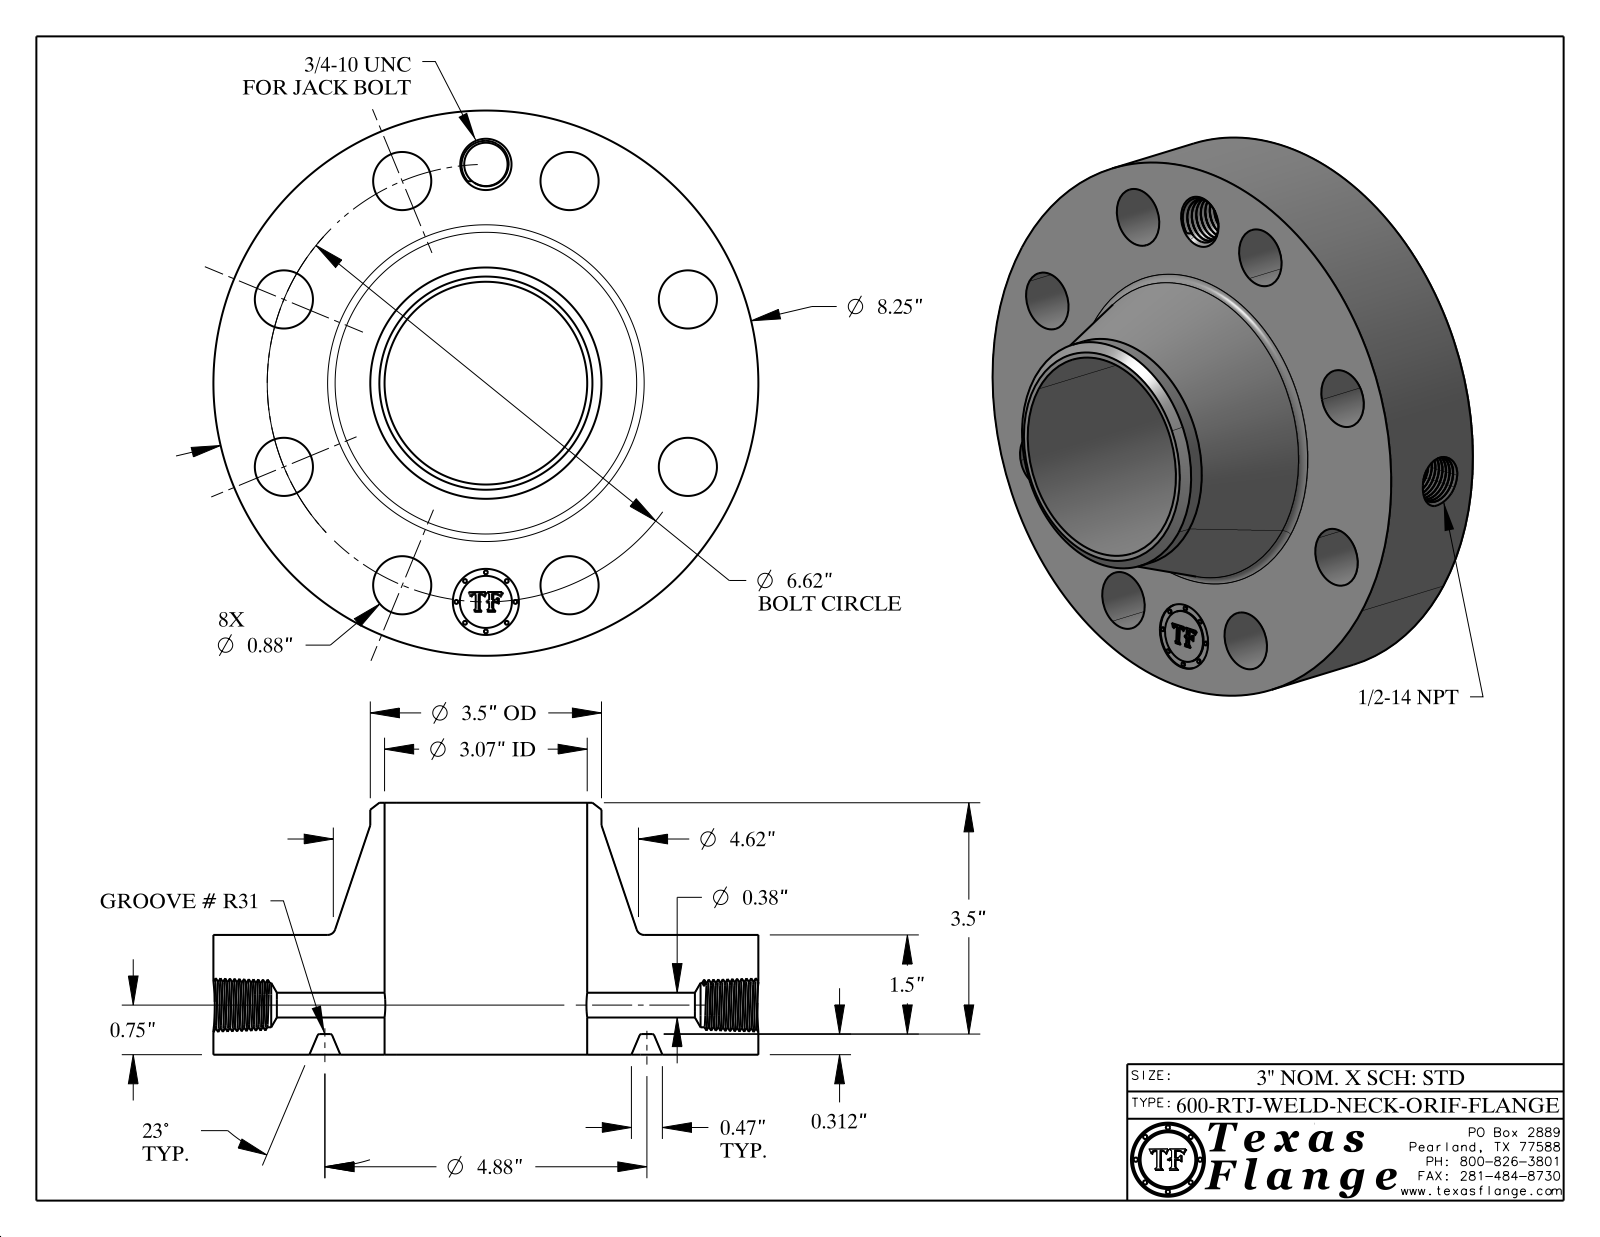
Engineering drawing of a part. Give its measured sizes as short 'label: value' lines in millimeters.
name: 600-RTJ-WELD-NECK
written by: CATIA V5 STEP AP214 (AUTOMOTIVE_DESIGN)
unit: mm
bodies: 1 solid, 795 faces (370 planar, 96 cylindrical, 329 other)
size: 209.6 × 209.6 × 96.8
volume: 1 331 000 mm³; area: 158 400 mm²
holes: 8× ⌀22.4, 1× ⌀9.5, 1× ⌀16.7, 1× ⌀17.1, 1× ⌀25.4, 1× ⌀77.9
bosses: 8× ⌀1.5, 1× ⌀209.6, 1× ⌀88.9, 1× ⌀20
face distances: 46, 7.9, 38.1, 96.8, 88.9, 50.8, 0.4, 45.6, 37.7, 51.2
hole spacings: 84.1, 118.9, 155.3, 168.1, 32.8, 64.3, 64.3, 93.4
